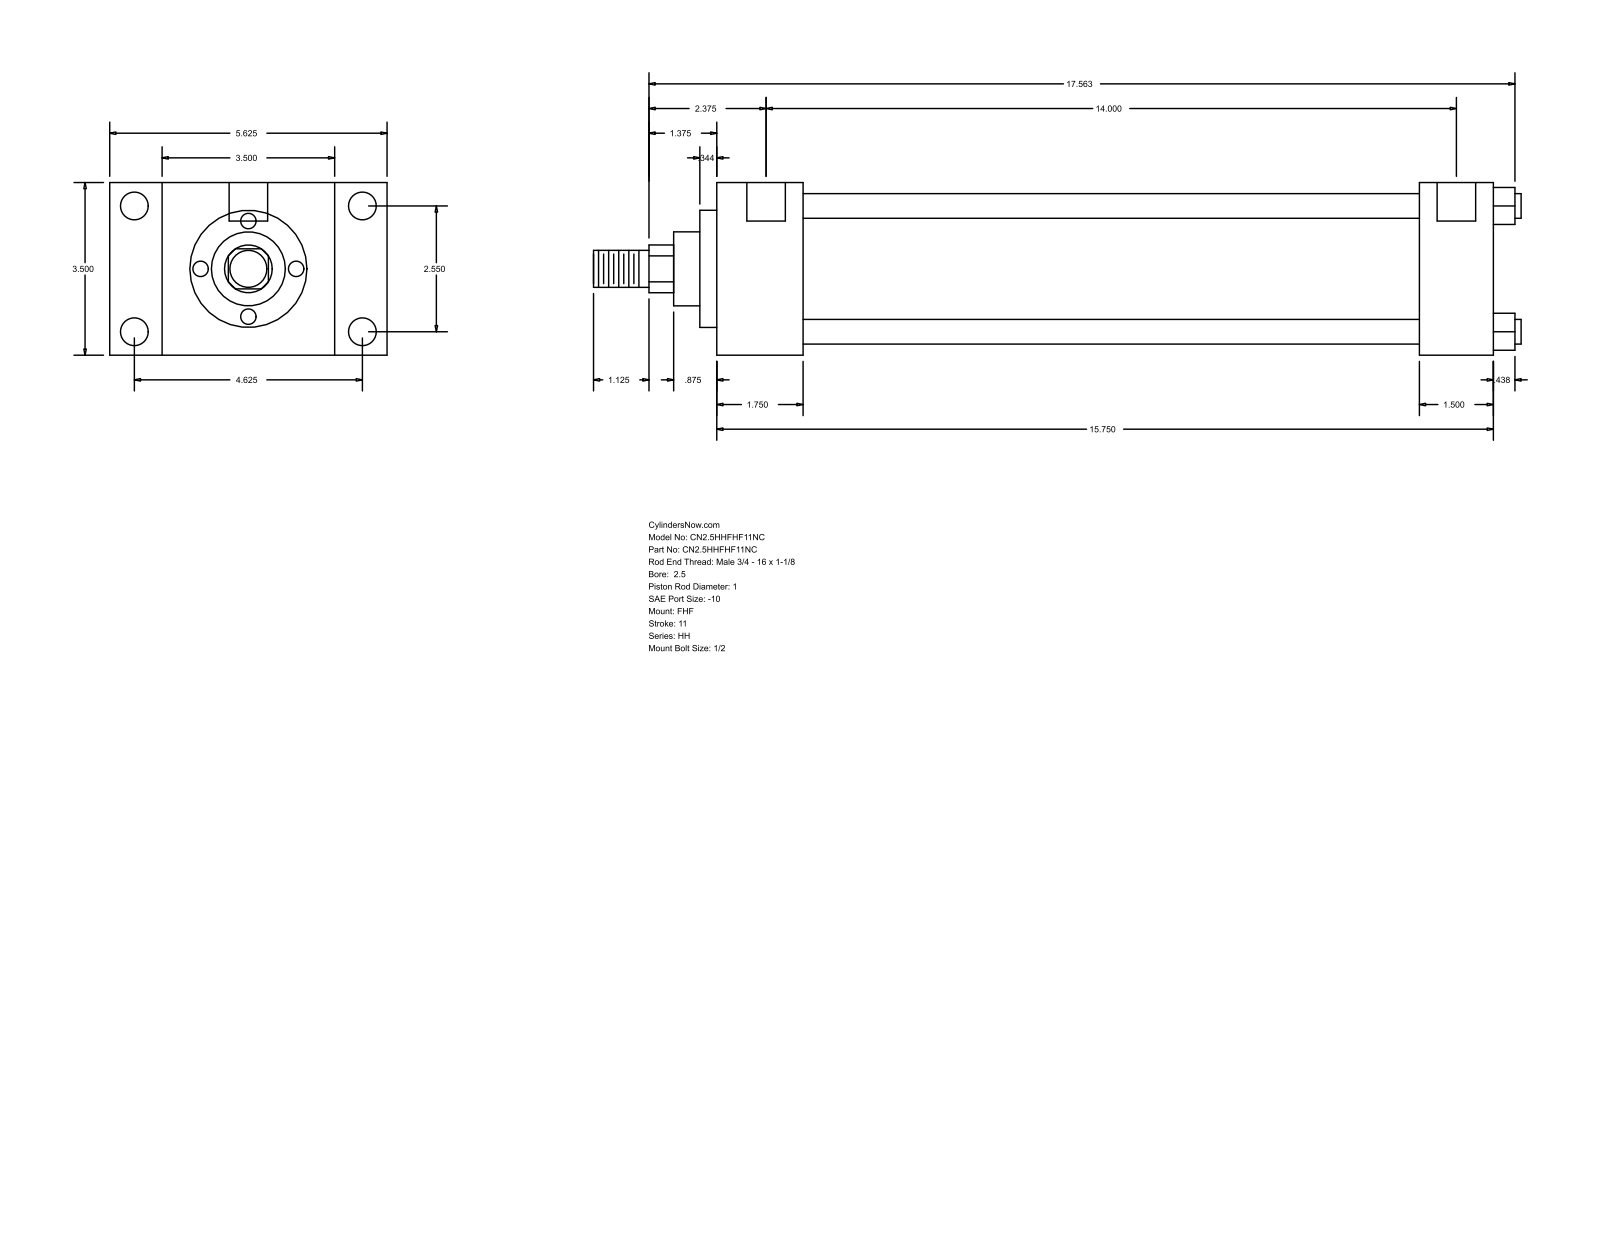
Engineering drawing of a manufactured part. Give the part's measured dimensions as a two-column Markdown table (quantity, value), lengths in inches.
| quantity | value |
| --- | --- |
| part name | HH_FHF__0250_1 |
| STEP written by | GSSL Pune (CONFIG_CONTROL_DESIGN) |
| units | inches |
| bodies | 0 solids, 90 faces (61 planar, 29 cylindrical, 0 other) |
| overall size | 18.813 × 5.625 × 3.5 |
| round holes (diameter × count) | 0.219 × 4, 0.563 × 4, 0.781 × 2 |
| round bosses / shafts (diameter × count) | 0.5 × 4, 2.875 × 1, 2.375 × 1, 1.5 × 1, 1 × 1, 0.75 × 1 |
| partial cylindrical surfaces (radius × count) | 0.484 × 1 |
| main face-to-face distances | 3.5, 1.75, 1.063, 4.563, 15.75, 14, 5.625, 1.5, 14.25, 12.5 |
| hole center spacings | 2.55, 4.625, 5.281, 14.125, 0.062, 0.063, 14, 14.062 |
